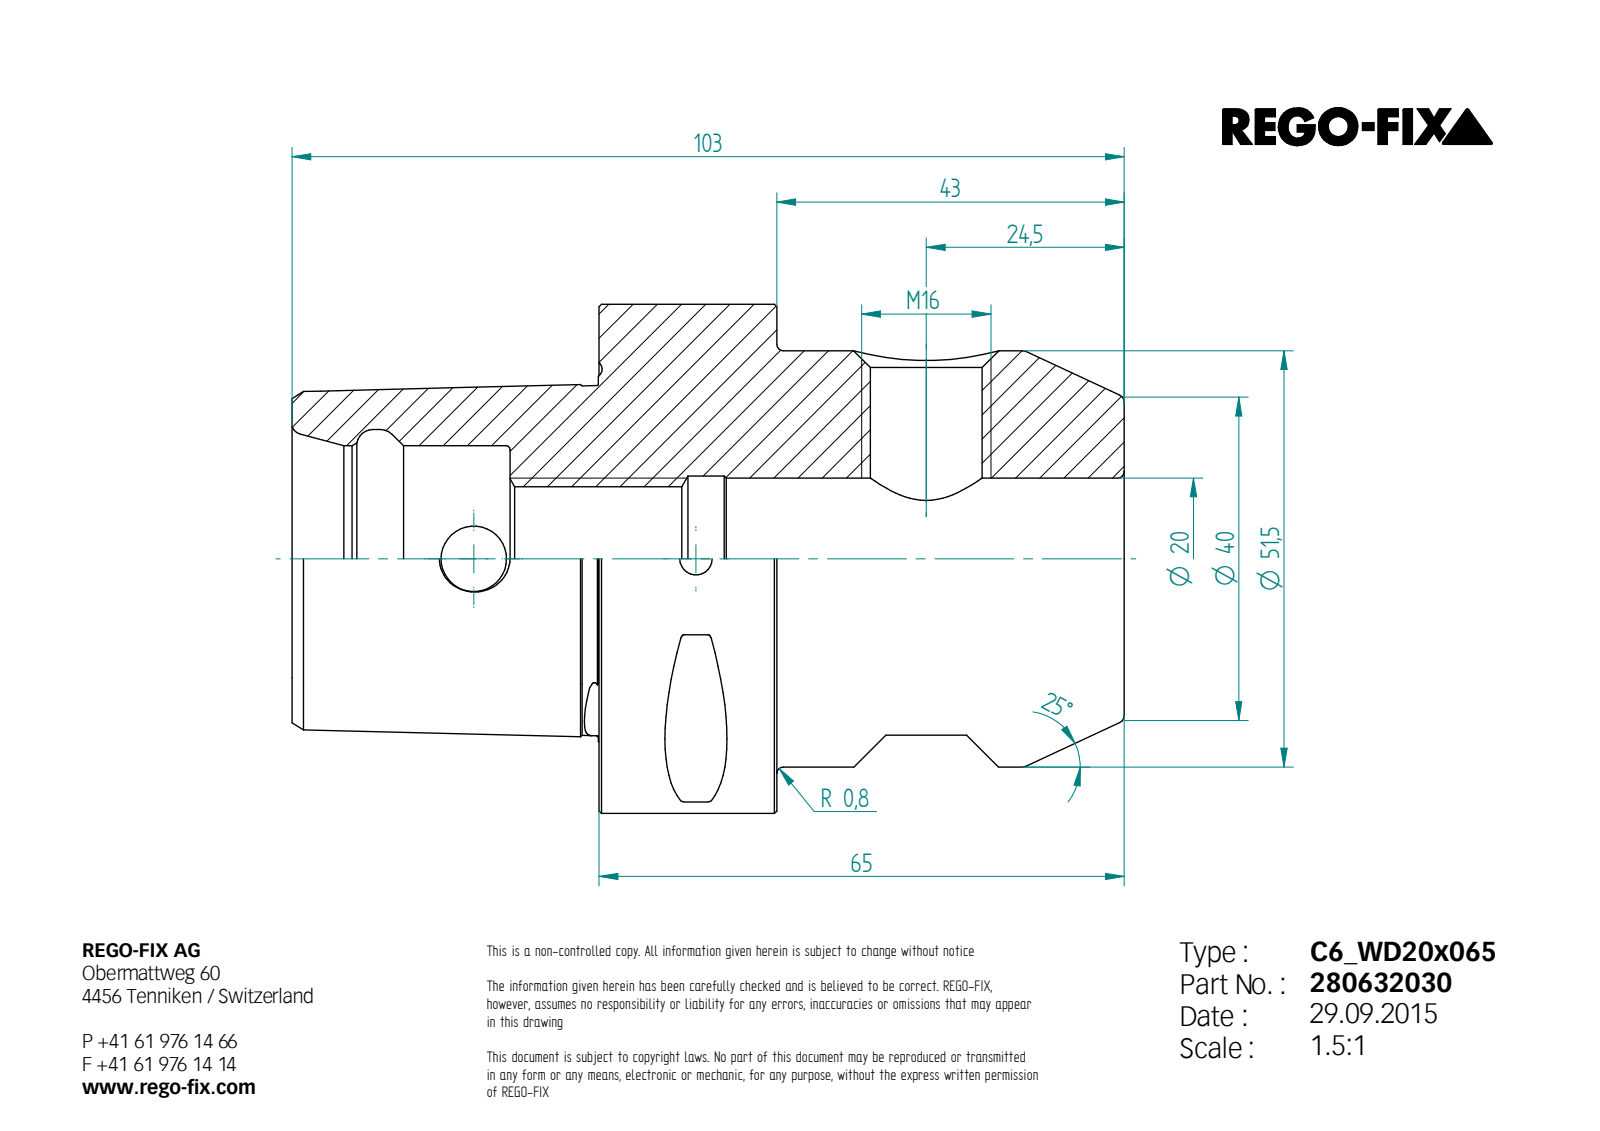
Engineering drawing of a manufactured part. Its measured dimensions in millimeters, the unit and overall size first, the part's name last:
Units: millimetres
Overall size (bounding box): 103 × 63 × 63
Round holes (diameter × count): ⌀4 ×1, ⌀8.1 ×1, ⌀13.84 ×1, ⌀17.84 ×1, ⌀20 ×1, ⌀20.5 ×1, ⌀28 ×1, ⌀32 ×1
Round bosses / shafts (diameter × count): ⌀63 ×1, ⌀51.5 ×1
Partial cylindrical surfaces — rounded edges, fillets, slot ends (radius × count): R0.5 ×8
Main face-to-face distances: 22, 65, 43, 38, 60, 103, 24.89, 27, 11, 33
Hole centre spacings: 27.5
Volume: 161 174 mm³ · Surface area: 28 981 mm²
Bodies: 1 solid, 109 faces (23 planar, 20 cylindrical, 66 other)
STEP written by: Unknown (AUTOMOTIVE_DESIGN)
